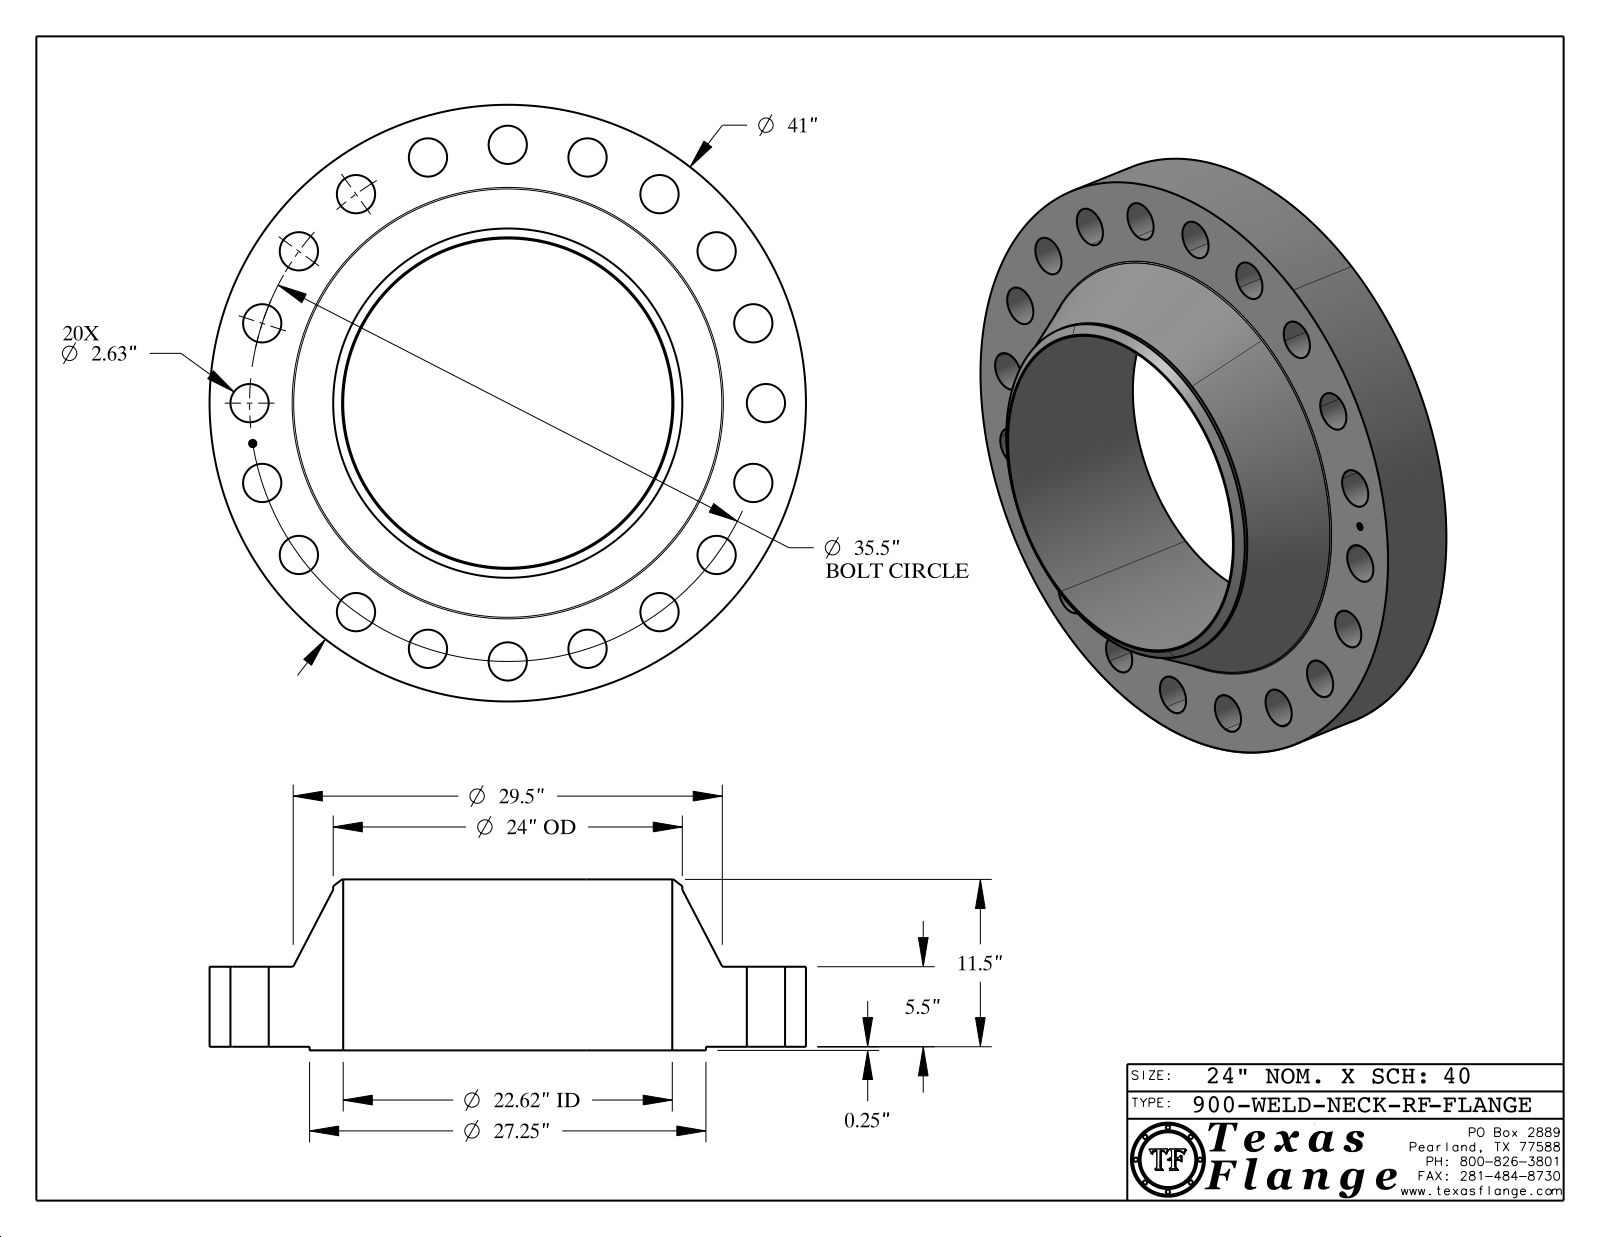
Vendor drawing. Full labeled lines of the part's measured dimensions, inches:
Part name (STEP PRODUCT): 900-WELD-NECK-RF
STEP written by: CATIA V5 STEP AP214 (AUTOMOTIVE_DESIGN)
Units: inches
Bodies: 1 solid, 443 faces (369 planar, 68 cylindrical, 6 other)
Overall size (bounding box): 41 × 41 × 11.75
Volume: 5 381 in³ · Surface area: 4 392 in²
Round holes (diameter × count): ⌀2.63 ×20, ⌀0.495 ×1, ⌀22.624 ×1
Round bosses / shafts (diameter × count): ⌀0.03 ×8, ⌀41 ×1, ⌀27.25 ×1, ⌀24 ×1, ⌀0.39 ×1
Main face-to-face distances: 5.5, 0.25, 5.75, 11.75, 11.5, 6, 5.735, 5.485, 0.015, 6.015
Hole centre spacings: 17.75, 10.97, 28.72, 31.631, 16.117, 20.866, 25.102, 33.762
